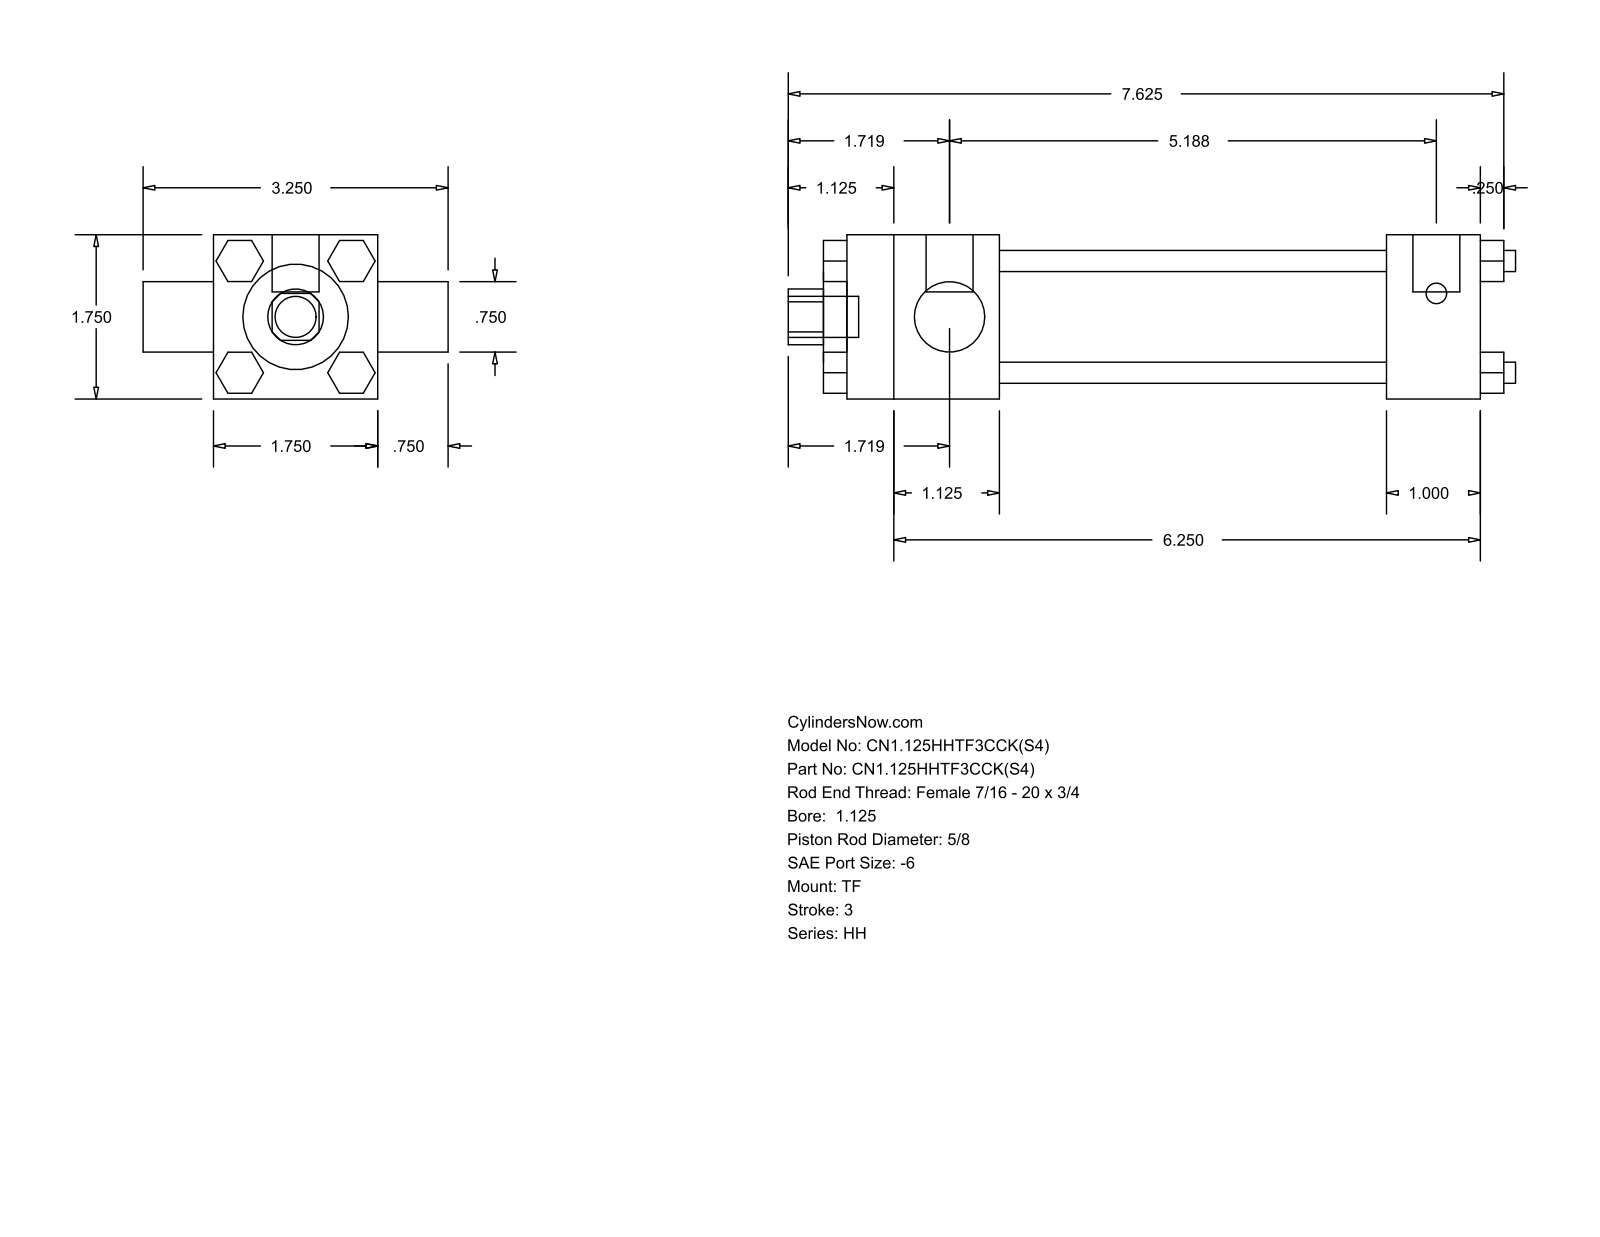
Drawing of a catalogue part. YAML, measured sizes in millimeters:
part_name: "HH_TF__0112_0.625"
step_written_by: "GSSL Pune (CONFIG_CONTROL_DESIGN)"
units: millimeters
bodies: {solids: 0, faces: 120, planar: 92, cylindrical: 28, other: 0}
overall_size: [196.85, 82.55, 44.45]
round_holes:
  - {diameter: 15.88, count: 1}
  - {diameter: 19.05, count: 1}
  - {diameter: 28.57, count: 1}
  - {diameter: 34.92, count: 1}
round_bosses_or_shafts:
  - {diameter: 5.71, count: 4}
  - {diameter: 5.56, count: 3}
  - {diameter: 12.7, count: 2}
  - {diameter: 11.11, count: 1}
partial_cylinders:
  - {radius: 7.54, count: 1}
face_to_face_distances: [44.46, 11.11, 104.78, 130.17, 25.39, 41.27, 146.05, 171.44, 47.62, 6.35]
